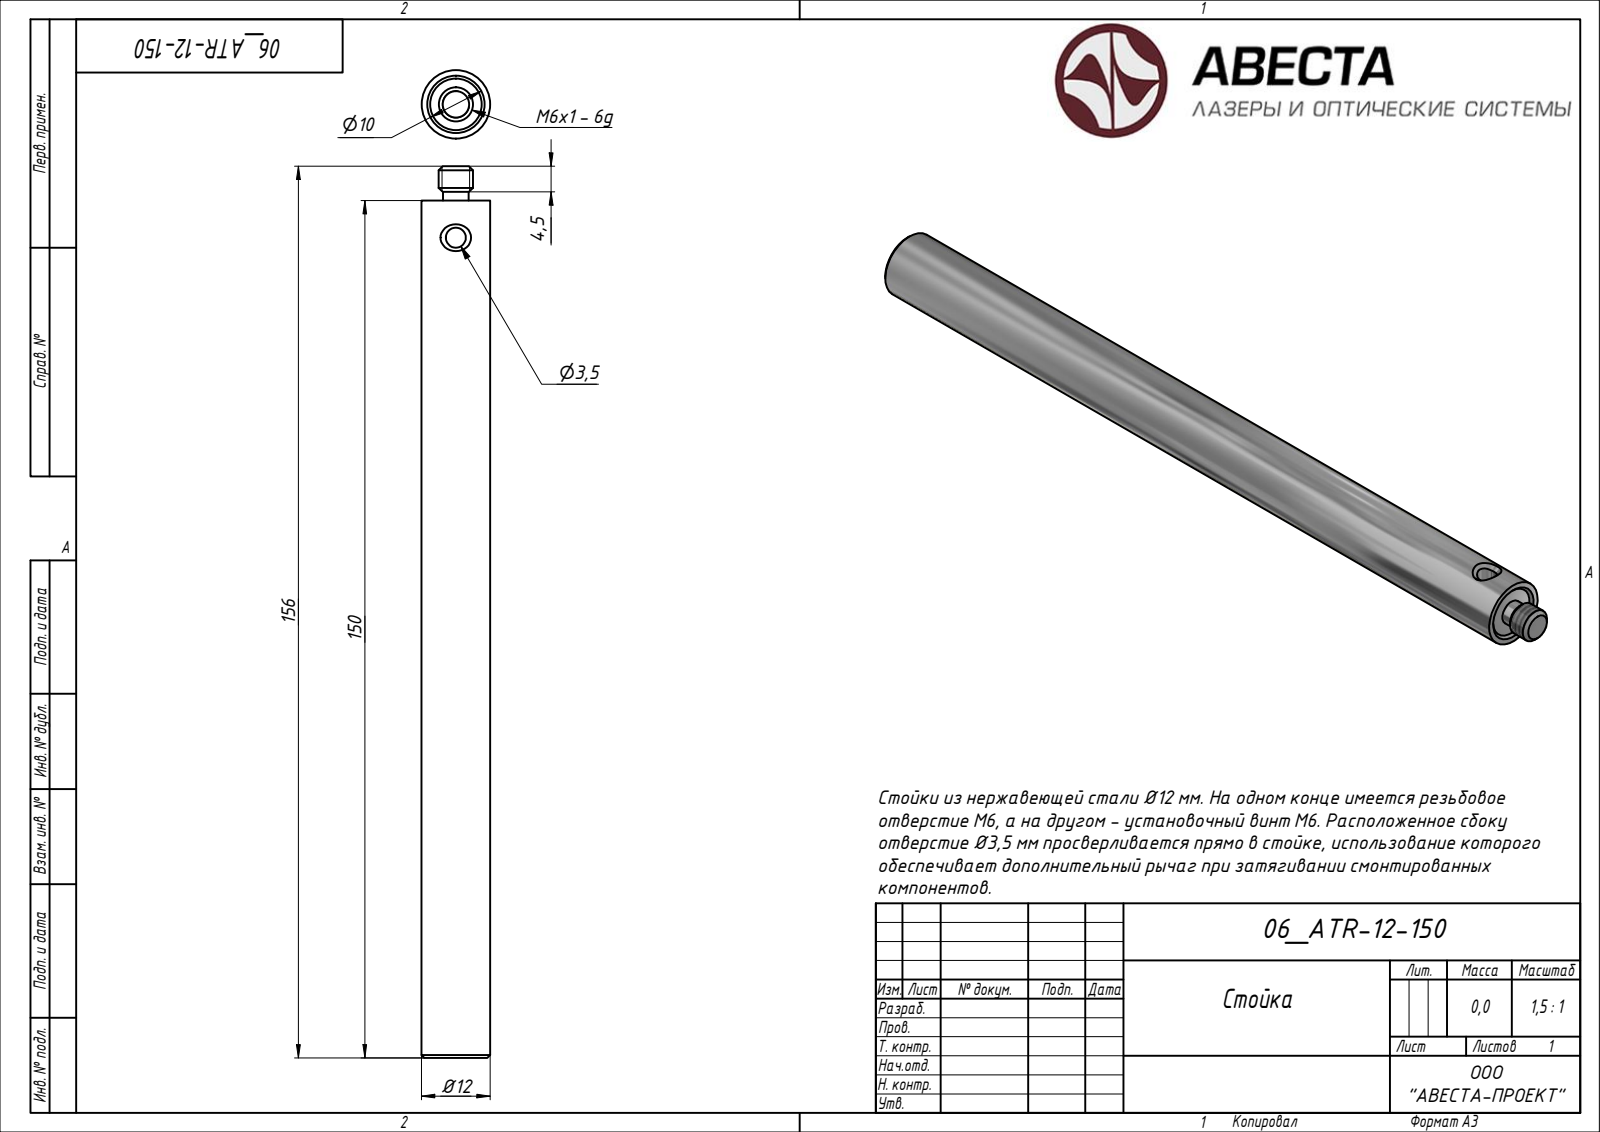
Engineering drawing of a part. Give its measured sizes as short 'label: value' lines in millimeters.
written by: ST-DEVELOPER v15 (AUTOMOTIVE_DESIGN)
unit: mm
bodies: 7 solids, 217 faces (35 planar, 0 cylindrical, 182 other)
size: 156.12 × 135.46 × 12
volume: 50 591 mm³; area: 21 493 mm²
face distances: 0.5, 40.28, 120.12, 79.84, 30.15, 59.97, 29.82, 10.13, 20.16, 70.1
